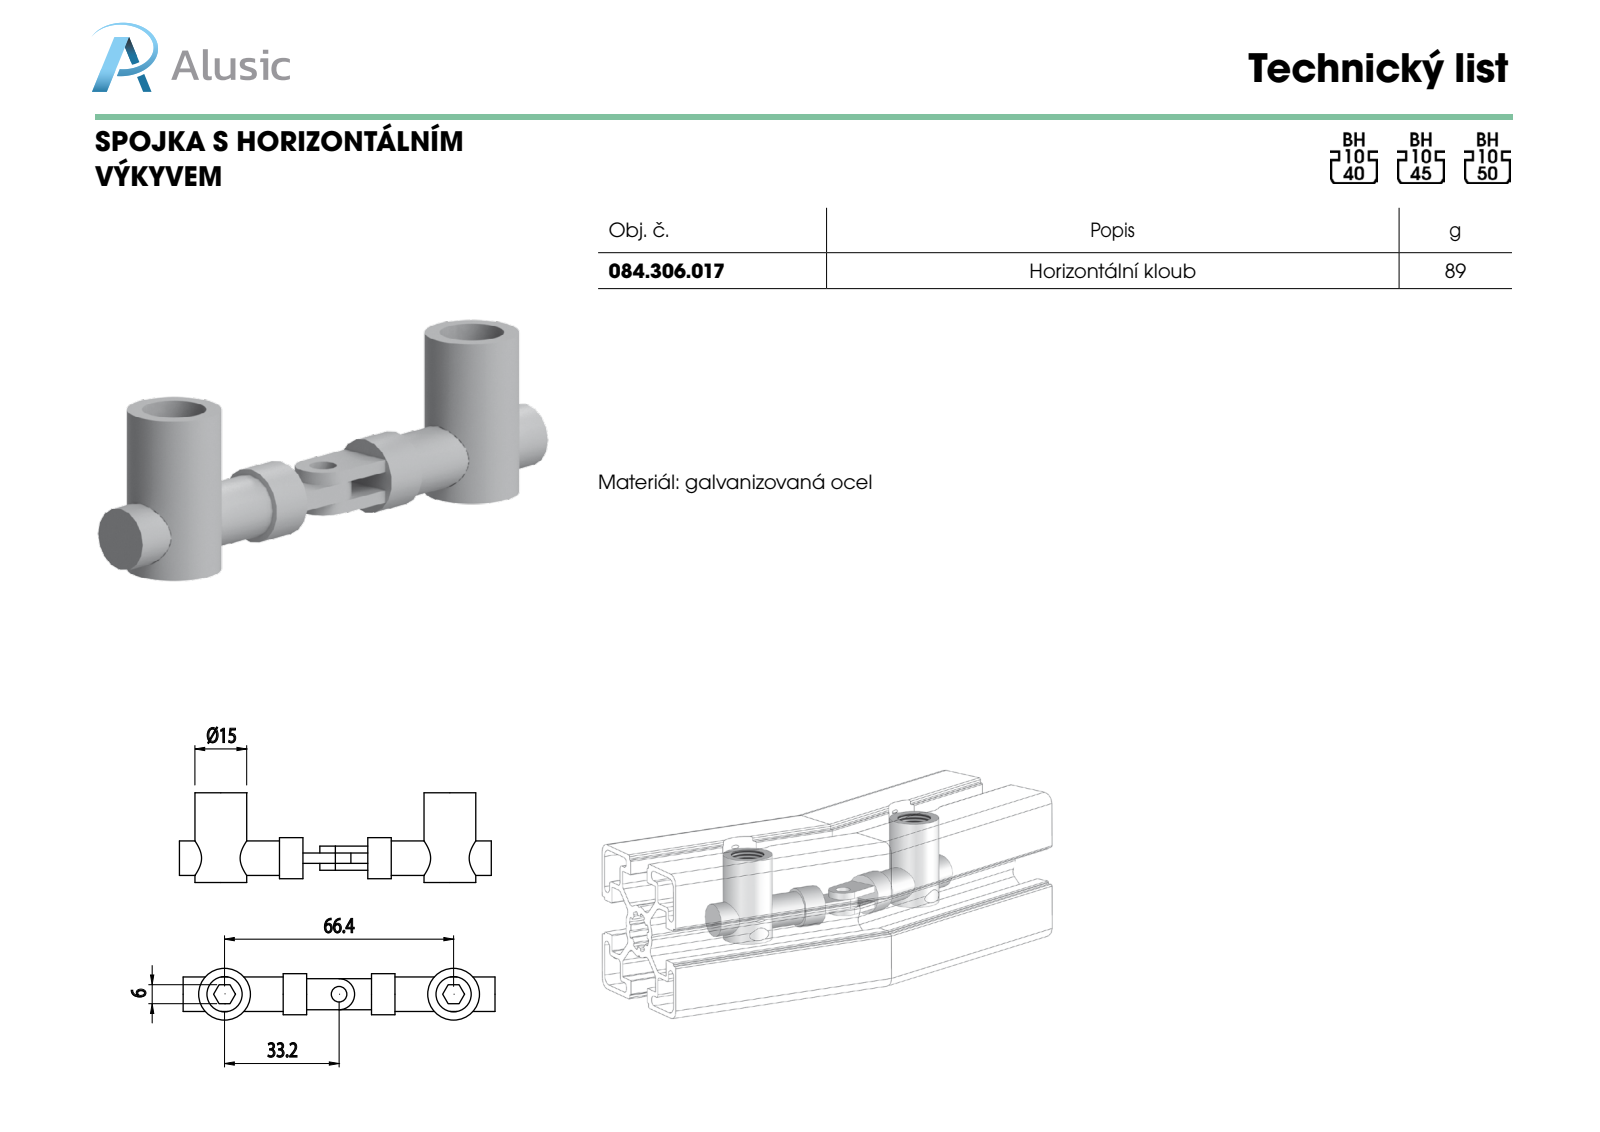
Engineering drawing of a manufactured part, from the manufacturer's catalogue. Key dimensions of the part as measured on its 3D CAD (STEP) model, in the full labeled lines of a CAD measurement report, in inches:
Part name (STEP PRODUCT): 1.JNT.002A; 1.JNT.002C; 1.JNT.002B; 084.306.017
STEP written by: SolidWorks 2012 (CONFIG_CONTROL_DESIGN)
Units: inches
Bodies: 4 solids, 59 faces (22 planar, 31 cylindrical, 6 other)
Overall size (bounding box): 3.559 × 1.024 × 0.591
Volume: 0.692 in³ · Surface area: 12.3 in²
Round holes (diameter × count): ⌀0.402 ×2, ⌀0.177 ×1, ⌀0.394 ×1
Round bosses / shafts (diameter × count): ⌀0.591 ×2, ⌀0.469 ×1, ⌀0.354 ×1
Main face-to-face distances: 0.219, 0.337, 0.079, 0.197, 0.118, 1.024, 0.805, 0.687, 1.409, 2.15
Hole centre spacings: 1.307, 2.614
